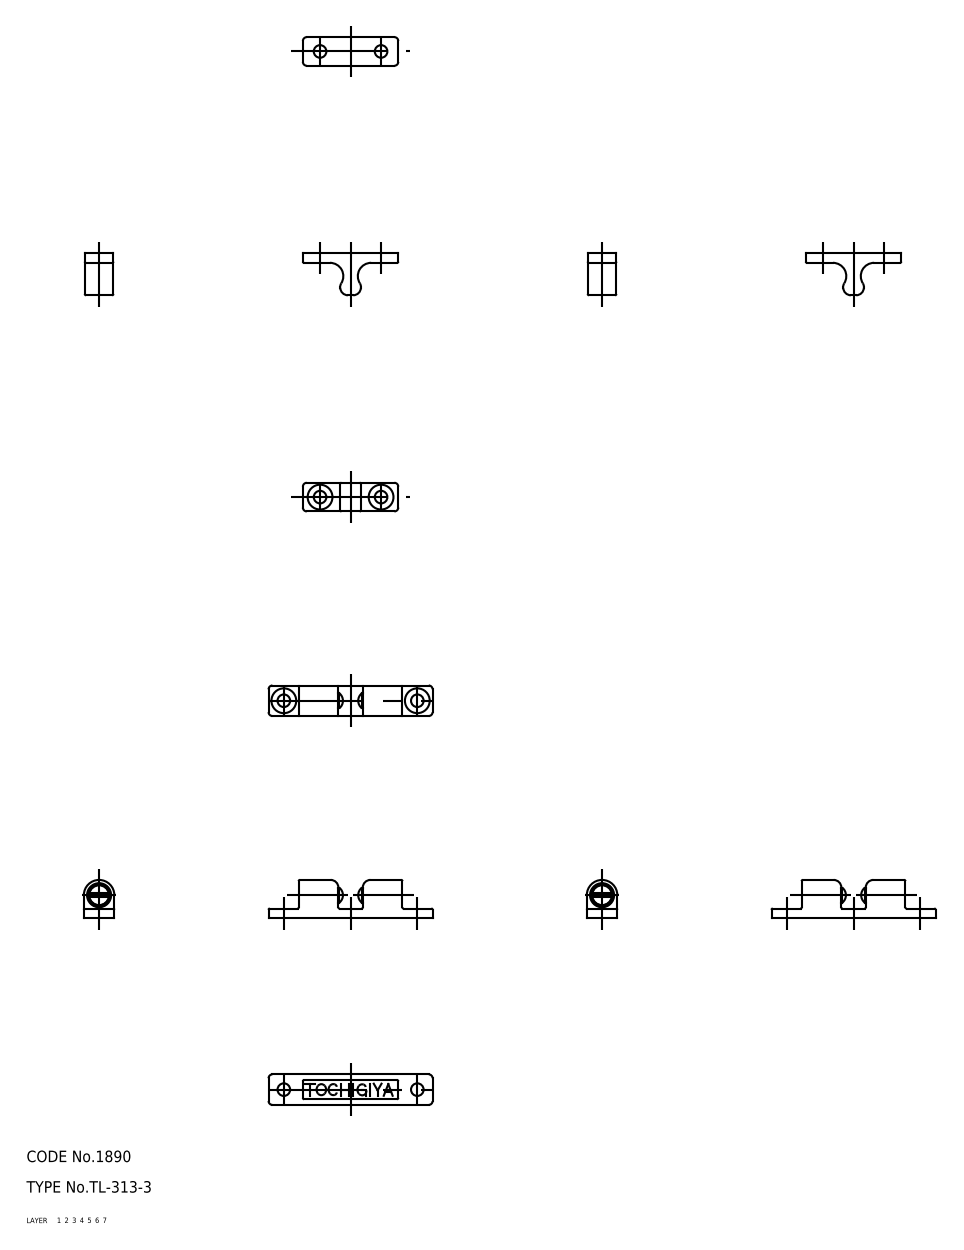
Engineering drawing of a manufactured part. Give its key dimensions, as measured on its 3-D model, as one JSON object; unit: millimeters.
{"part_name": "screw; ball; keeper; housing (+1 more)", "step_written_by": "CADfix (AUTOMOTIVE_DESIGN)", "units": "millimeters", "bodies": {"solids": 6, "faces": 94, "planar": 0, "cylindrical": 0, "other": 94}, "overall_size": [43, 40.8, 8], "volume_mm3": 2511, "surface_area_mm2": 2847}
